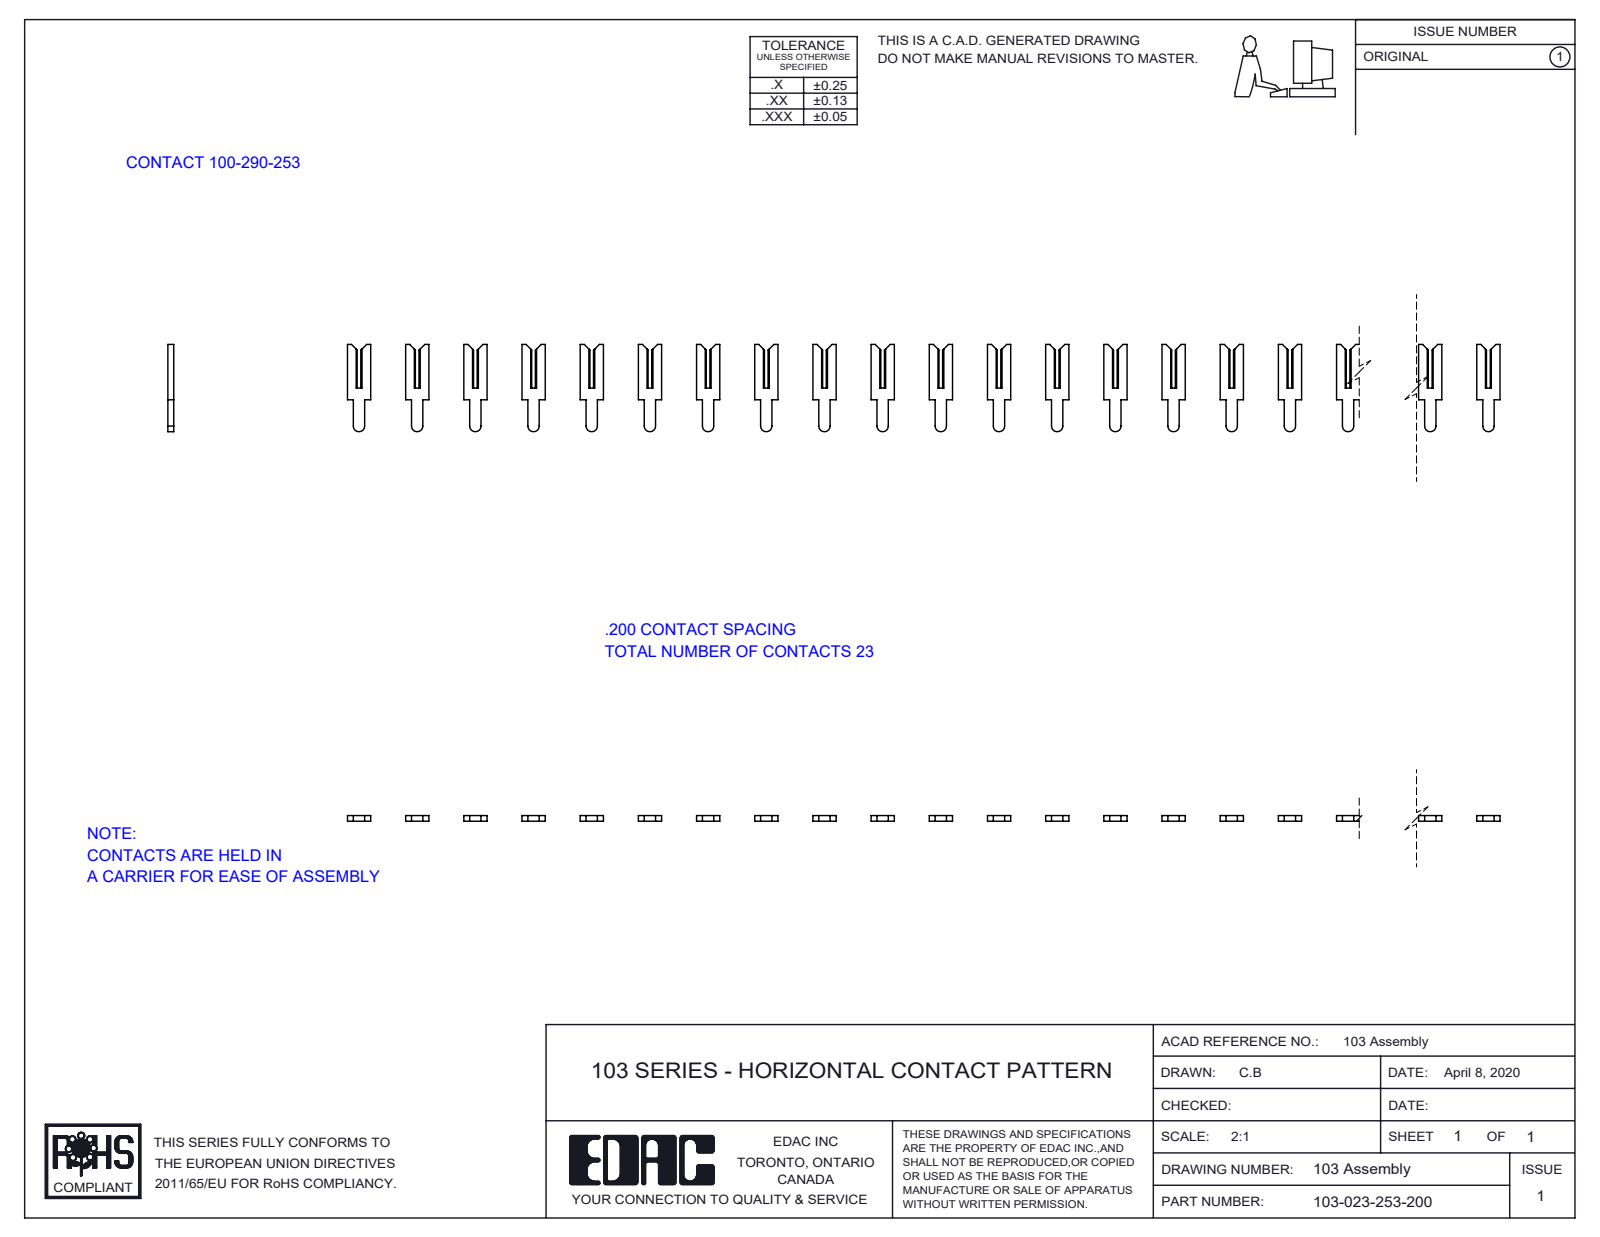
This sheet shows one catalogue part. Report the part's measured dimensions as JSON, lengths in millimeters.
{"part_name": "100-290-001_100-290-253; 103-023-253-200", "step_written_by": "SolidWorks 2016 (CONFIG_CONTROL_DESIGN)", "units": "millimeters", "bodies": {"solids": 23, "faces": 460, "planar": 437, "cylindrical": 23, "other": 0}, "overall_size": [113.8, 7.6, 0.5], "volume_mm3": 100, "surface_area_mm2": 792, "partial_cylinders_radius": [[0.5, 23]], "face_to_face_distances": [0.5, 5.1, 10.2, 15.2, 20.3, 3.6, 25.4, 30.5, 35.6, 21.5]}
